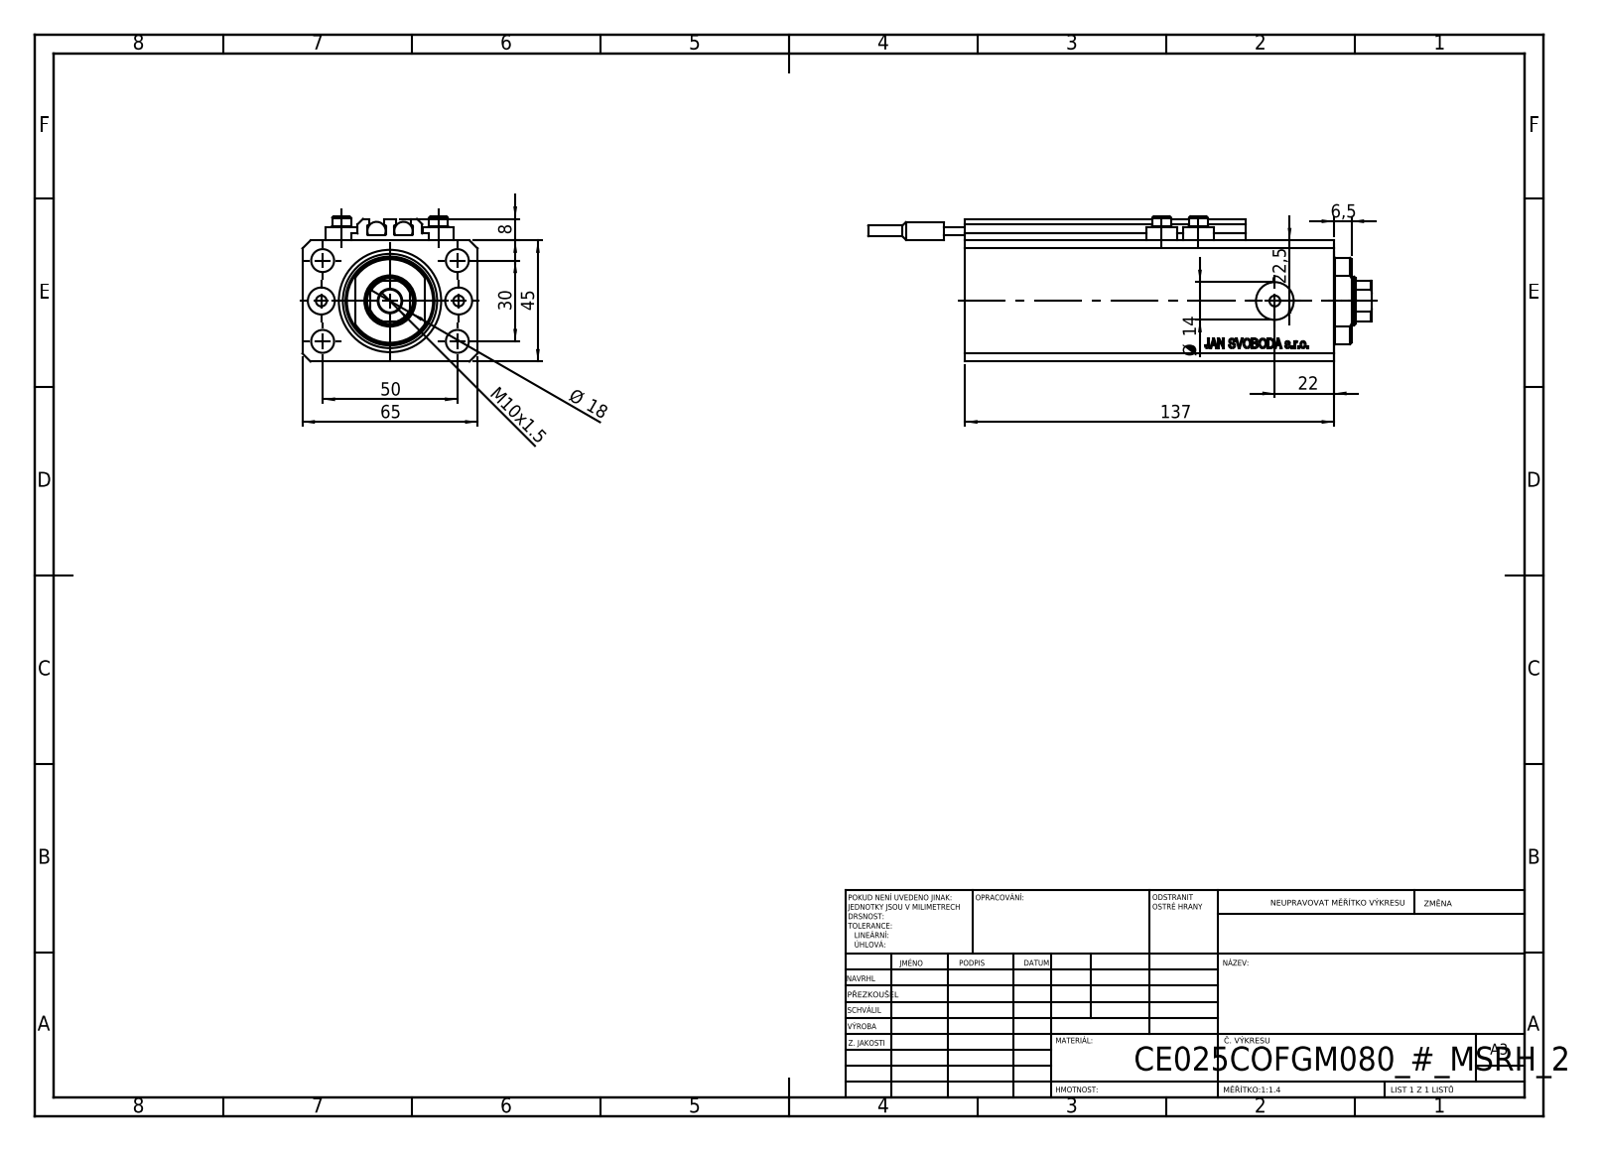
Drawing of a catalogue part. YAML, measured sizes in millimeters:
part_name: "V250CE_C_VCP; V250CE_C_Body; SWITCH_V250CE; ALLEN BOLT V250CE (+1 more)"
step_written_by: "SolidWorks 2019 (CONFIG_CONTROL_DESIGN)"
units: millimeters
bodies: {solids: 10, faces: 1086, planar: 536, cylindrical: 98, other: 452}
overall_size: [187, 65, 54]
volume: 369700
surface_area: 93356
round_holes:
  - {diameter: 4, count: 8}
  - {diameter: 8.5, count: 5}
  - {diameter: 10, count: 2}
  - {diameter: 14, count: 2}
  - {diameter: 18, count: 1}
  - {diameter: 25, count: 1}
  - {diameter: 38, count: 1}
round_bosses_or_shafts:
  - {diameter: 11.6, count: 4}
  - {diameter: 7, count: 4}
  - {diameter: 6.8, count: 2}
  - {diameter: 6.5, count: 2}
  - {diameter: 4, count: 2}
partial_cylinders:
  - {radius: 0.2, count: 10}
  - {radius: 8.5, count: 1}
  - {radius: 16, count: 1}
face_to_face_distances: [45, 65, 47, 14, 2, 123, 2.5, 3, 137, 10]
hole_center_spacings: [15.01, 29.15, 52.68, 13.6, 25.5, 30, 36, 38.48]
